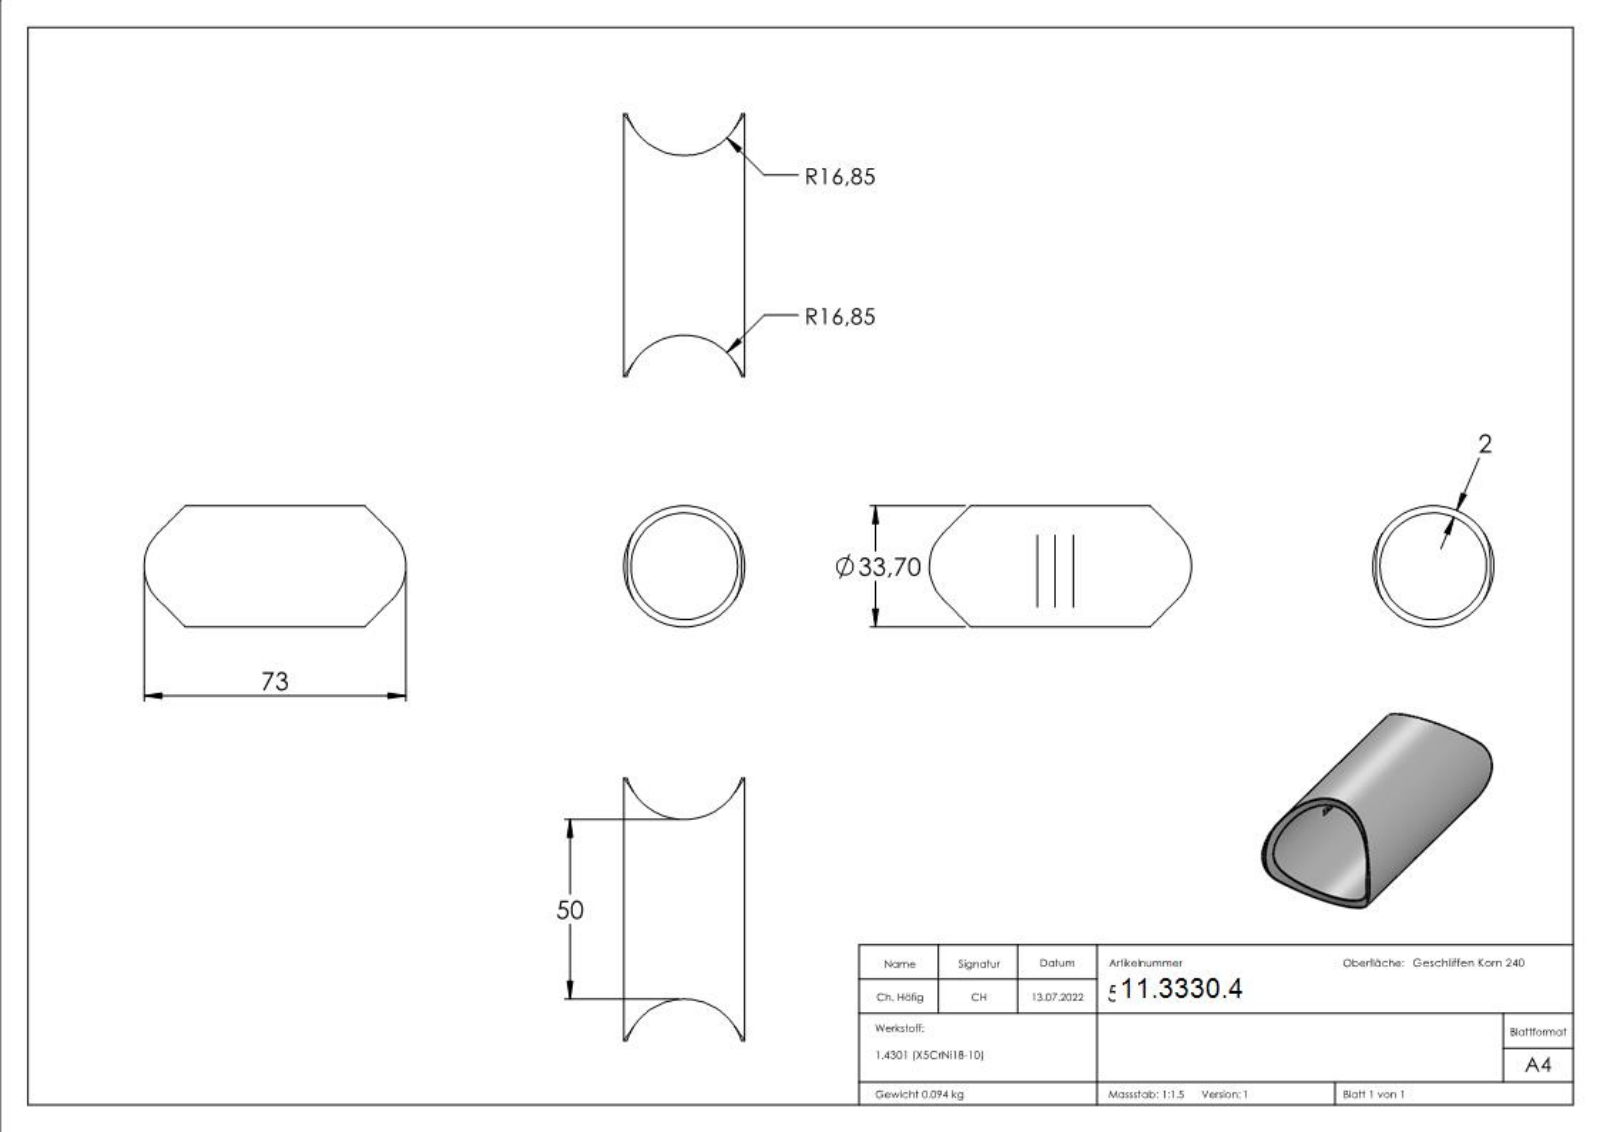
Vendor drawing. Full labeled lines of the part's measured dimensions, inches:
Part name (STEP PRODUCT): 50450-240
STEP written by: SolidWorks 2018 (CONFIG_CONTROL_DESIGN)
Units: inches
Bodies: 1 solid, 275 faces (124 planar, 34 cylindrical, 117 other)
Overall size (bounding box): 2.874 × 1.327 × 1.327
Volume: 0.725 in³ · Surface area: 19.29 in²
Round holes (diameter × count): ⌀1.169 ×1
Round bosses / shafts (diameter × count): ⌀1.327 ×1
Partial cylindrical surfaces — rounded edges, fillets, slot ends (radius × count): R0.509 ×2, R0.663 ×2, R0.589 ×1
Main face-to-face distances: 0.173, 0.072, 0.114, 0.035, 0.129, 0.036, 0.013, 0.108, 0.305, 0.087
